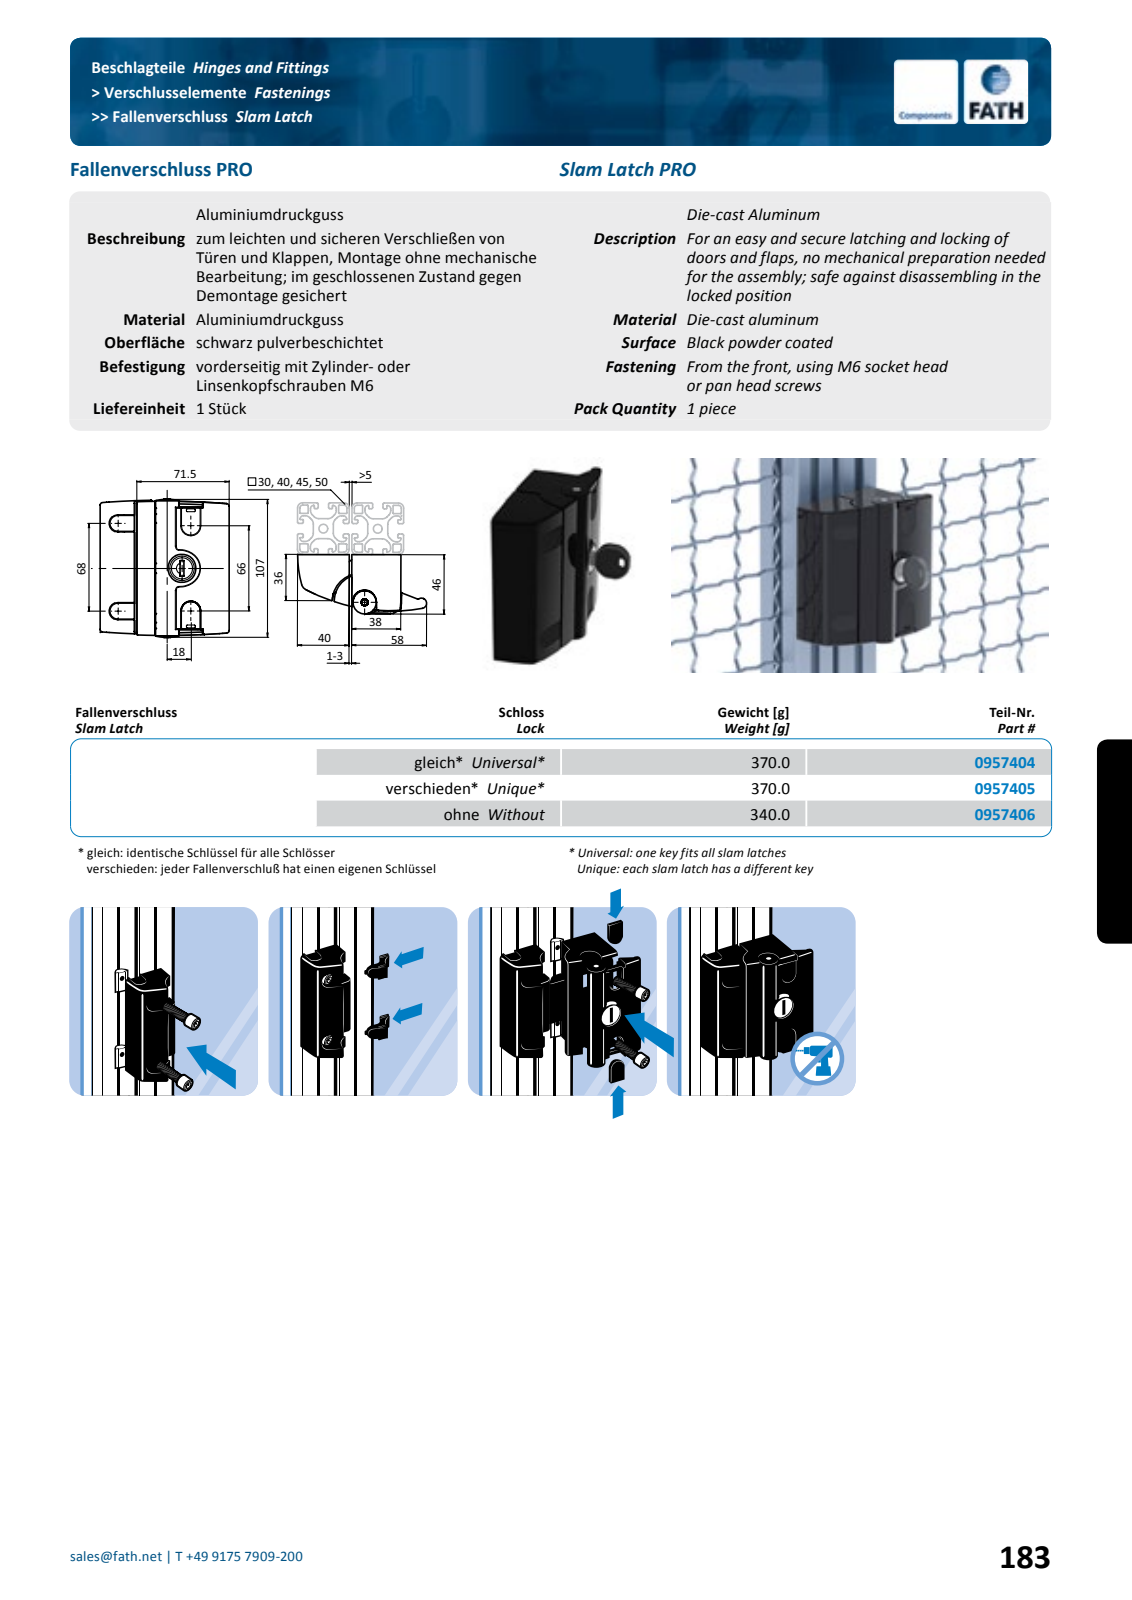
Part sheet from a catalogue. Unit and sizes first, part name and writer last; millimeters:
Units: millimetres
Overall size (bounding box): 106.85 × 100 × 46.5
Round holes (diameter × count): ⌀5 ×1, ⌀5.1 ×1, ⌀6 ×1, ⌀17.2 ×1, ⌀21 ×1
Round bosses / shafts (diameter × count): ⌀20 ×1, ⌀18 ×1, ⌀11.6 ×1, ⌀9.9 ×1
Partial cylindrical surfaces — rounded edges, fillets, slot ends (radius × count): R0.5 ×178, R0.3 ×163, R1 ×129, R0.2 ×68, R0.1 ×50, R2 ×25, R0.7 ×20, R5 ×9
Main face-to-face distances: 2, 68, 38, 3.2, 9.8, 35, 4, 36, 34, 11.2
Volume: 126 410 mm³ · Surface area: 102 930 mm²
Bodies: 13 solids, 3627 faces (1231 planar, 1063 cylindrical, 1333 other)
Part name (STEP PRODUCT): fath_0957406_1; fath_0957406_2; fath_0957406_3; fath_0957406_4 (+8 more)
STEP written by: Spatial InterOp 3D (automotive_design)
